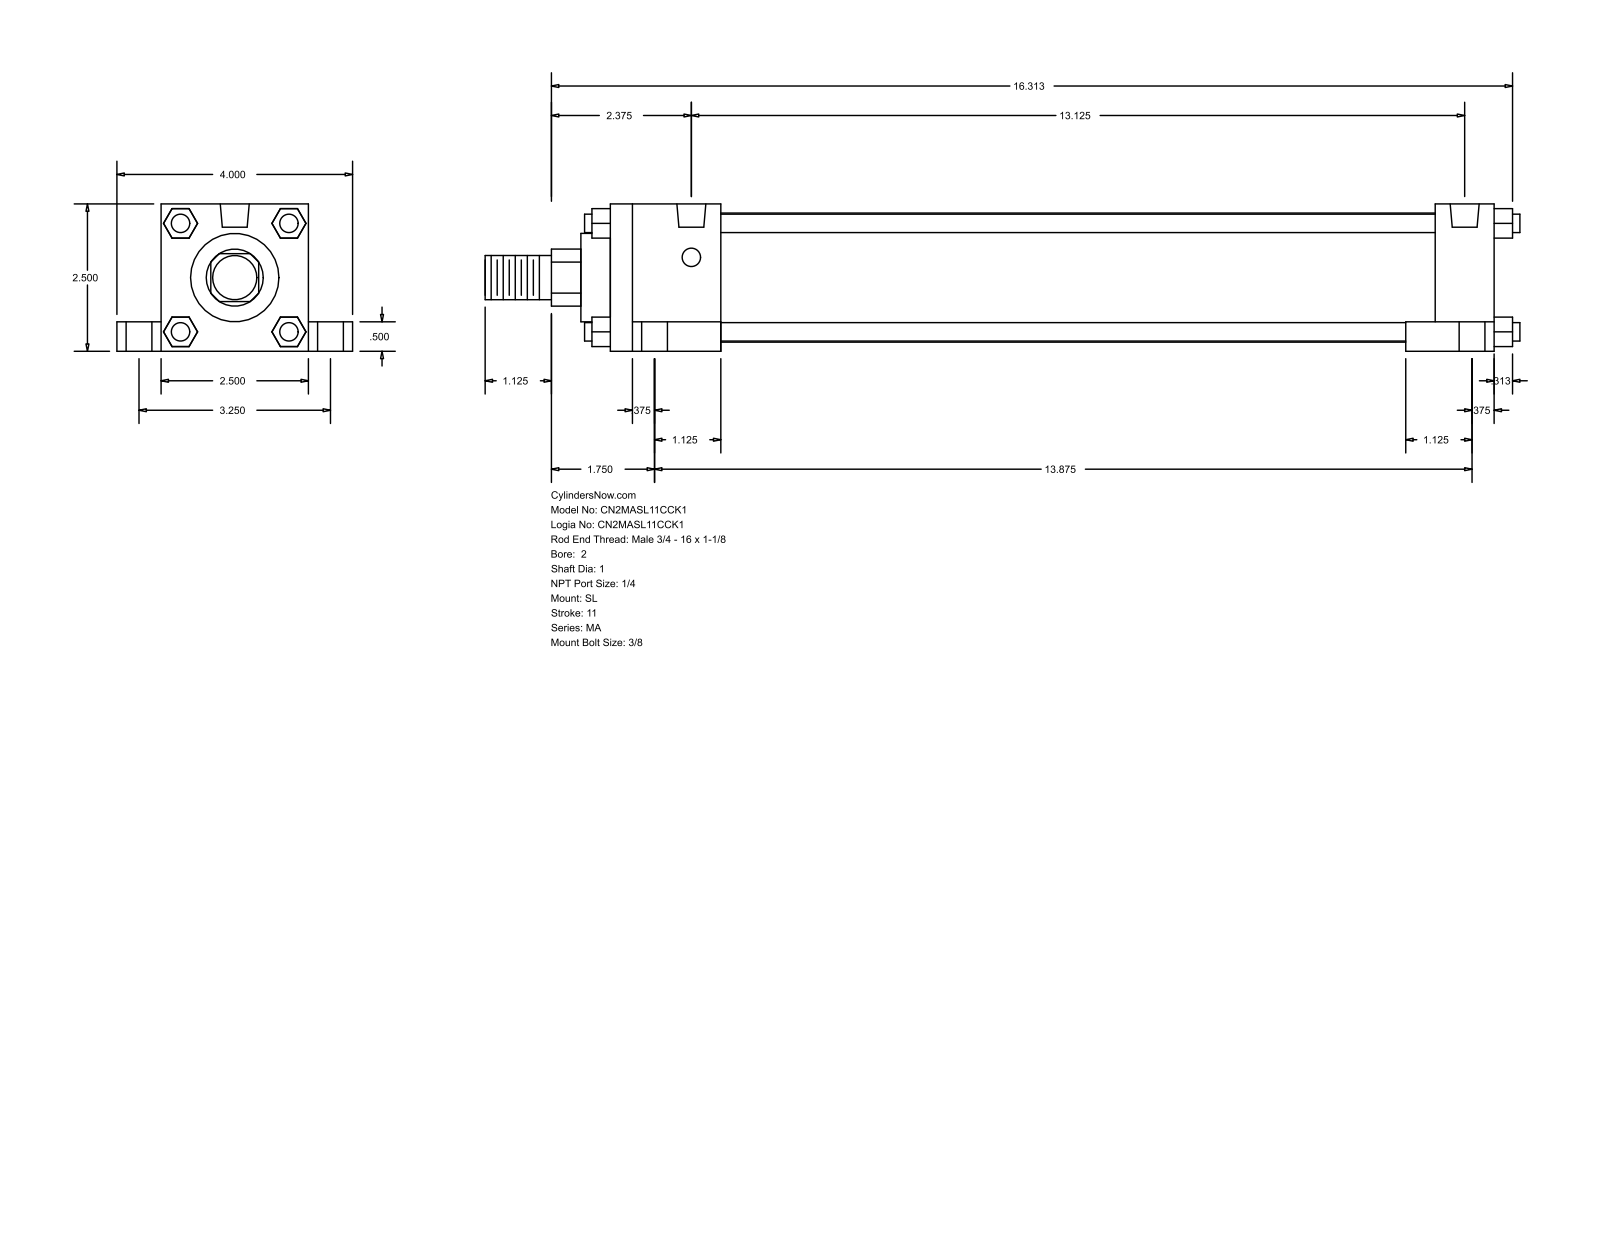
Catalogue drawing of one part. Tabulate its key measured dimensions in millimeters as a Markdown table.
| quantity | value |
| --- | --- |
| part name | MA_SL__0200_1 |
| STEP written by | GSSL Pune (CONFIG_CONTROL_DESIGN) |
| units | millimeters |
| bodies | 0 solids, 148 faces (112 planar, 36 cylindrical, 0 other) |
| overall size | 446.09 × 101.6 × 63.5 |
| round holes (diameter × count) | 7.94 × 4, 11.11 × 4, 17.46 × 4, 12.49 × 2 |
| round bosses / shafts (diameter × count) | 7.94 × 4, 55.63 × 1, 38.1 × 1, 25.4 × 1, 19.05 × 1 |
| partial cylindrical surfaces (radius × count) | 12.29 × 1 |
| main face-to-face distances | 63.5, 12.7, 381, 19.05, 82.55, 25.4, 50.8, 47.63, 333.37, 355.6 |
| hole center spacings | 41.39, 44.22, 82.54, 333.37, 339.07, 351.68, 352.43, 361.97 |
